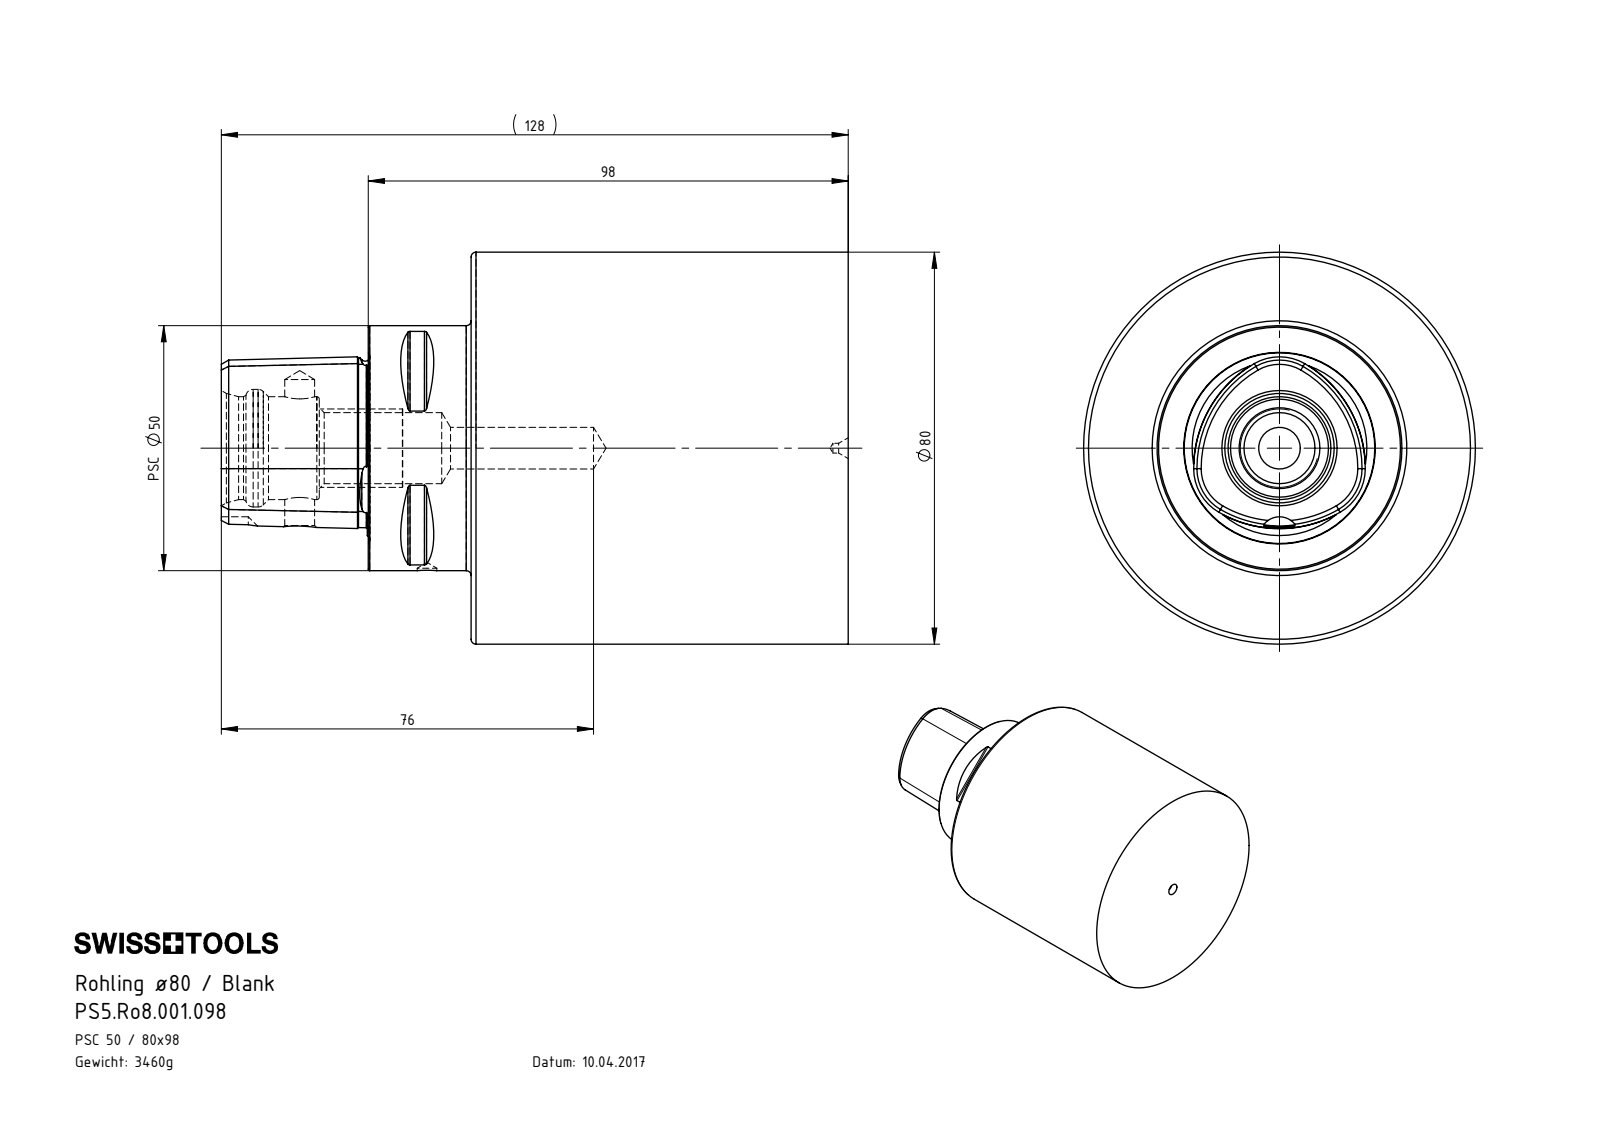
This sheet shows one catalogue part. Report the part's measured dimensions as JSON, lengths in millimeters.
{"part_name": "PS5.Ro8.001.098", "step_written_by": "SolidWorks 2017 (AUTOMOTIVE_DESIGN)", "units": "millimeters", "bodies": {"solids": 1, "faces": 95, "planar": 21, "cylindrical": 21, "other": 53}, "overall_size": [128, 80, 80], "volume_mm3": 440284, "surface_area_mm2": 39448, "round_holes": [[2, 1], [6.1, 1], [8.5, 1], [10, 1], [14.5, 1], [16.3, 1], [21, 1], [24, 1]], "round_bosses_or_shafts": [[80, 1], [50, 1]], "partial_cylinders_radius": [[0.5, 8], [5, 1]], "face_to_face_distances": [77, 21, 98, 30, 51, 128, 19.18, 44.4, 20, 10], "hole_center_spacings": [26]}
